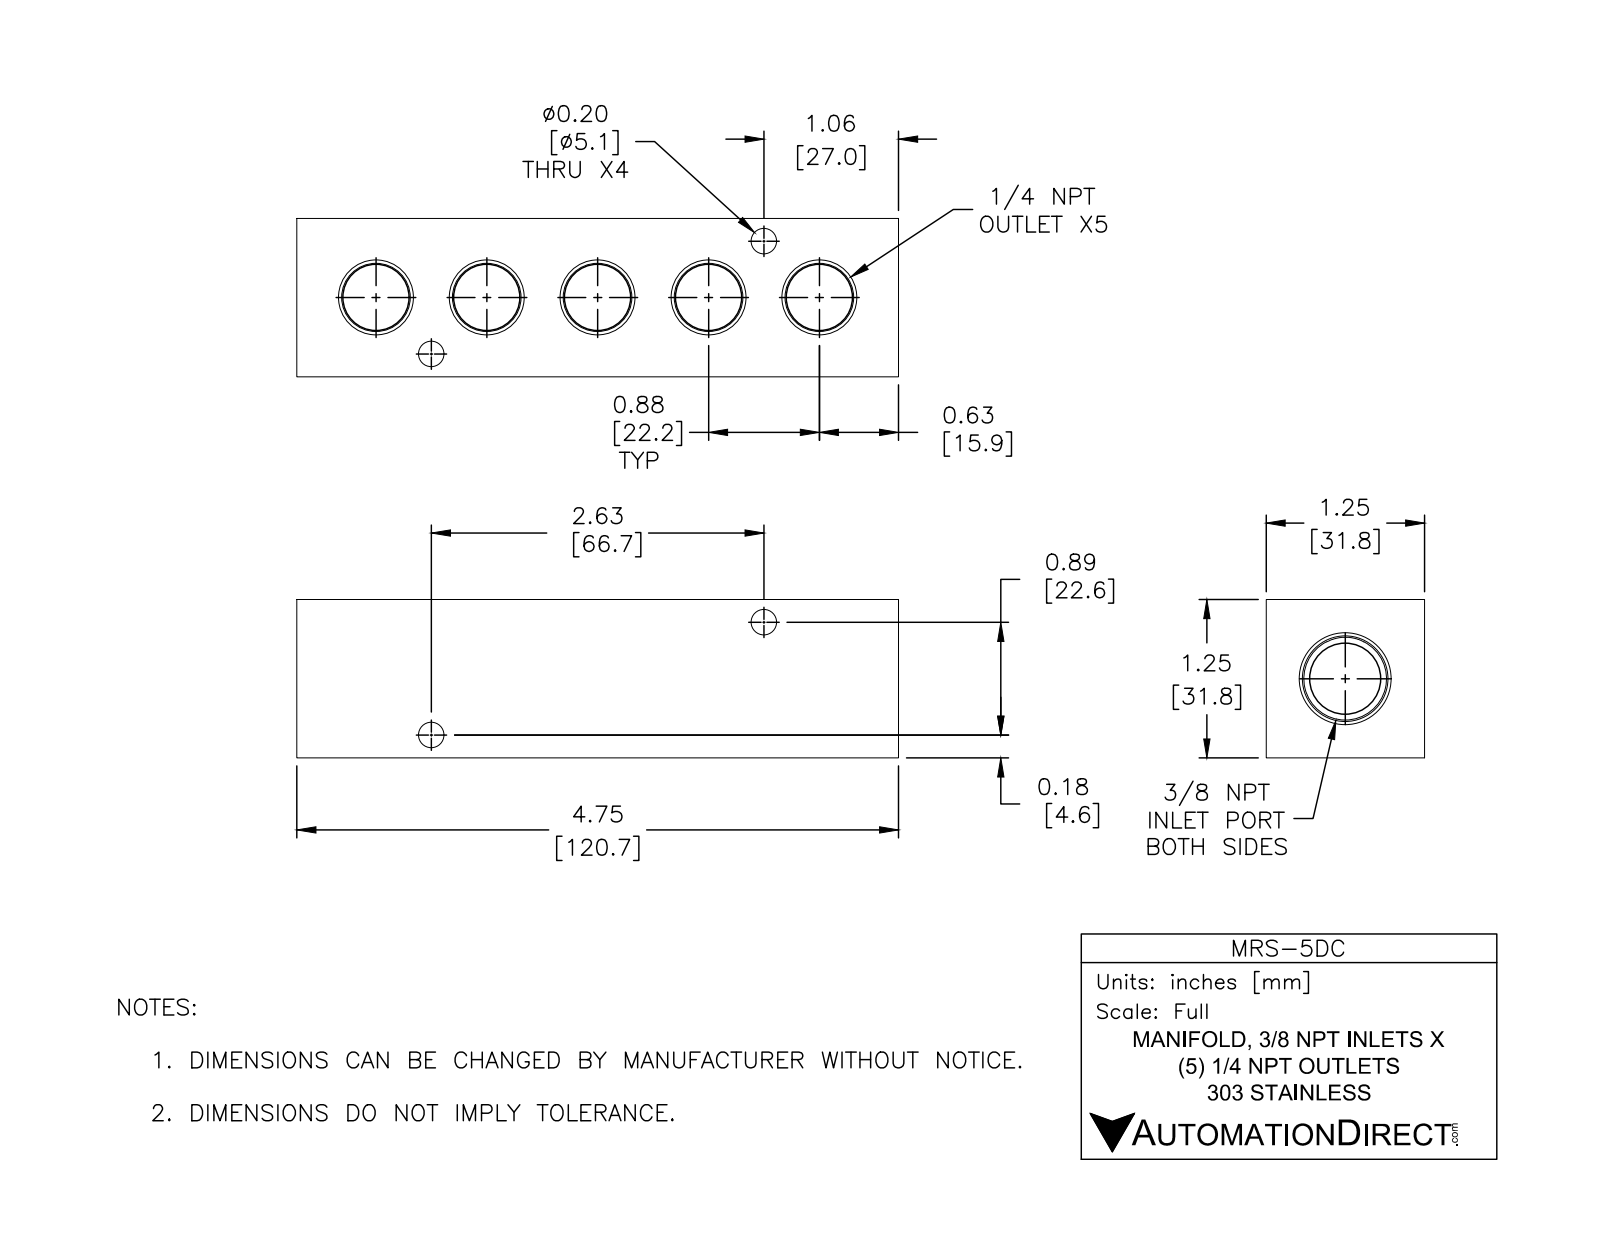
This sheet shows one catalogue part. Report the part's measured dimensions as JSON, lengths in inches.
{"part_name": "MRS-5DC", "step_written_by": "SolidWorks 2015 (CONFIG_CONTROL_DESIGN)", "units": "inches", "bodies": {"solids": 1, "faces": 74, "planar": 18, "cylindrical": 28, "other": 28}, "overall_size": [4.75, 1.25, 1.25], "volume_in3": 5.605, "surface_area_in2": 38.63, "round_holes": [[0.2, 4], [0.562, 1]], "partial_cylinders_radius": [[0.219, 5]], "face_to_face_distances": [1.25, 4.75, 0.86, 0.39, 0.41, 4.34, 3.93], "hole_center_spacings": [2.772]}
